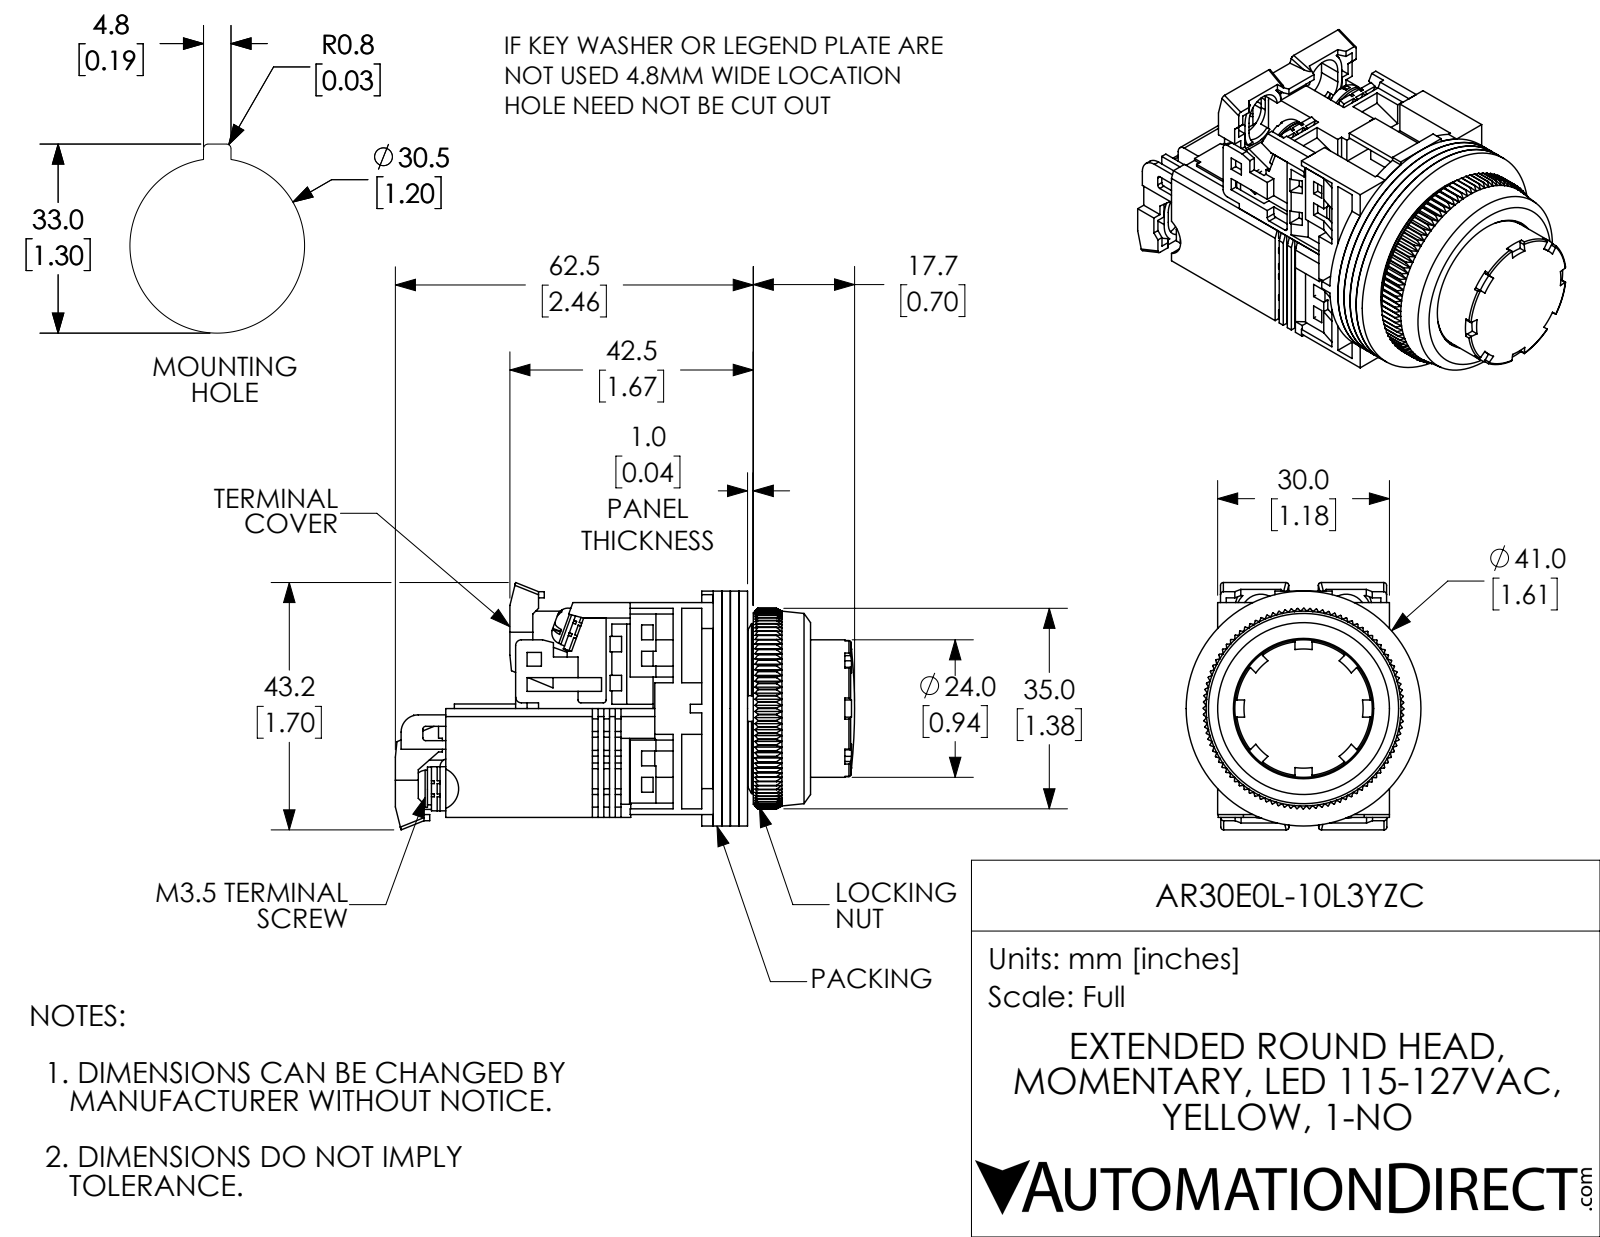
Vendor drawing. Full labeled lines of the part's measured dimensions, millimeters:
Part name (STEP PRODUCT): AR30E0L-10L3YZC
STEP written by: SolidWorks 2017 (AUTOMOTIVE_DESIGN)
Units: millimetres
Bodies: 27 solids, 1960 faces (1368 planar, 339 cylindrical, 253 other)
Overall size (bounding box): 80.2 × 43.2 × 41
Volume: 47 240 mm³ · Surface area: 41 310 mm²
Round holes (diameter × count): ⌀3.5 ×6, ⌀3.6 ×4, ⌀3 ×3, ⌀12 ×1, ⌀18 ×1, ⌀18.5 ×1, ⌀20 ×1, ⌀24 ×1, ⌀24.5 ×1, ⌀28.5 ×1, ⌀31.8 ×1
Round bosses / shafts (diameter × count): ⌀6.6 ×4, ⌀3.5 ×2, ⌀41 ×1, ⌀30 ×1, ⌀22 ×1, ⌀19.7 ×1, ⌀14 ×1
Partial cylindrical surfaces — rounded edges, fillets, slot ends (radius × count): R1.5 ×17, R0.3 ×16, R0.5 ×13, R3.5 ×4, R4.5 ×4, R1 ×2, R3 ×2, R0.4 ×1
Main face-to-face distances: 1.5, 3, 4.5, 19, 1, 0.5, 2, 36, 17.5, 1.2
Hole centre spacings: 14.7, 0.5, 7.5, 7.6, 7.6, 14.8, 14.8, 15.4
